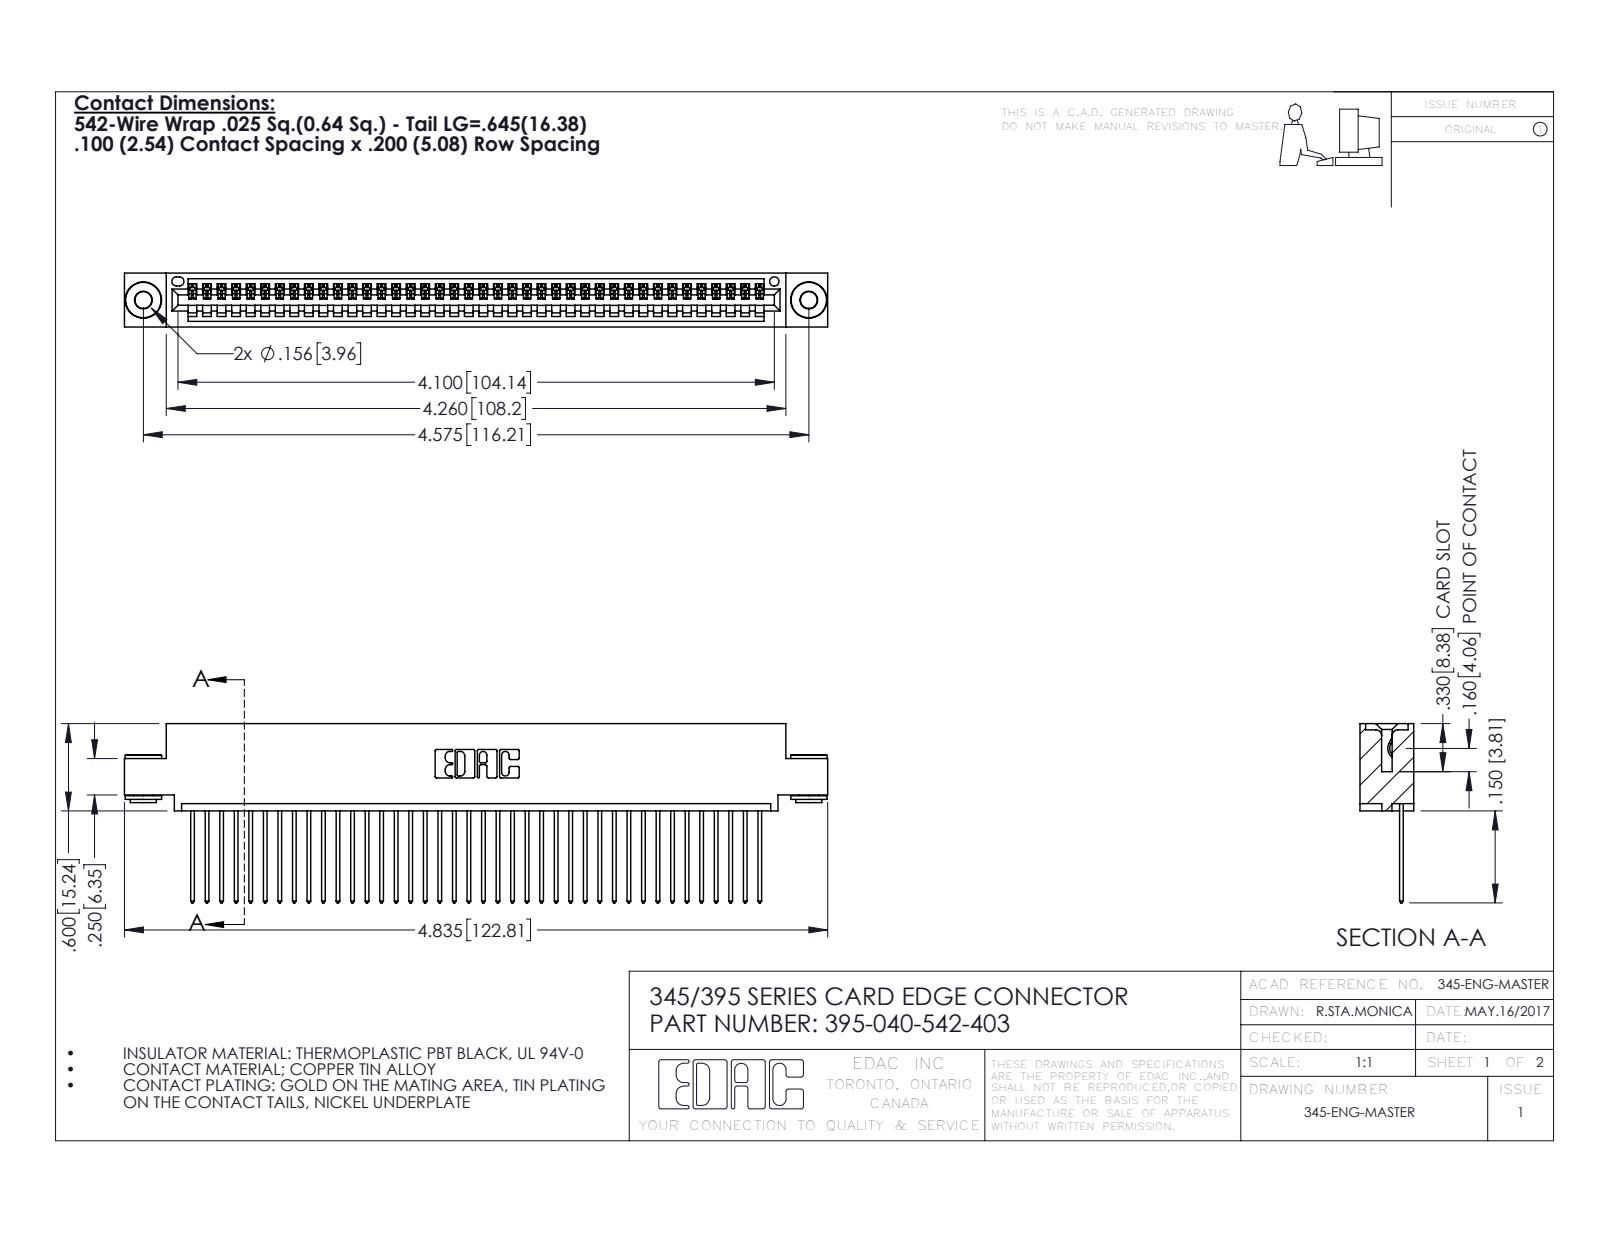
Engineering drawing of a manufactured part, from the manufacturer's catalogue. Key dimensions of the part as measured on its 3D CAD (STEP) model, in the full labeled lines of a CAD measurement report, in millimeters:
Part name (STEP PRODUCT): 395-040-542-403; 345-292-001_345-293-142; 345-250-002_345-250-002-102; 345 Part_0.110 Offset - 0.156 Dia-TH
STEP written by: SolidWorks 2016 (CONFIG_CONTROL_DESIGN)
Units: millimetres
Bodies: 43 solids, 2488 faces (1694 planar, 786 cylindrical, 8 other)
Overall size (bounding box): 122.8 × 31.3 × 9.4
Volume: 11 700 mm³ · Surface area: 16 350 mm²
Round holes (diameter × count): ⌀2.9 ×2, ⌀4 ×2, ⌀1.6 ×1
Round bosses / shafts (diameter × count): ⌀6.4 ×2, ⌀4.6 ×2, ⌀3.5 ×2
Partial cylindrical surfaces — rounded edges, fillets, slot ends (radius × count): R0.2 ×80, R0.3 ×80, R0.3 ×22, R0.2 ×6, R0.8 ×6, R0.7 ×3, R0.8 ×2, R1 ×2
Main face-to-face distances: 1.8, 7.6, 0.6, 9.4, 2.5, 6.9, 5.1, 5.7, 3.8, 1.8
Hole centre spacings: 6.9, 110.2, 116.2
